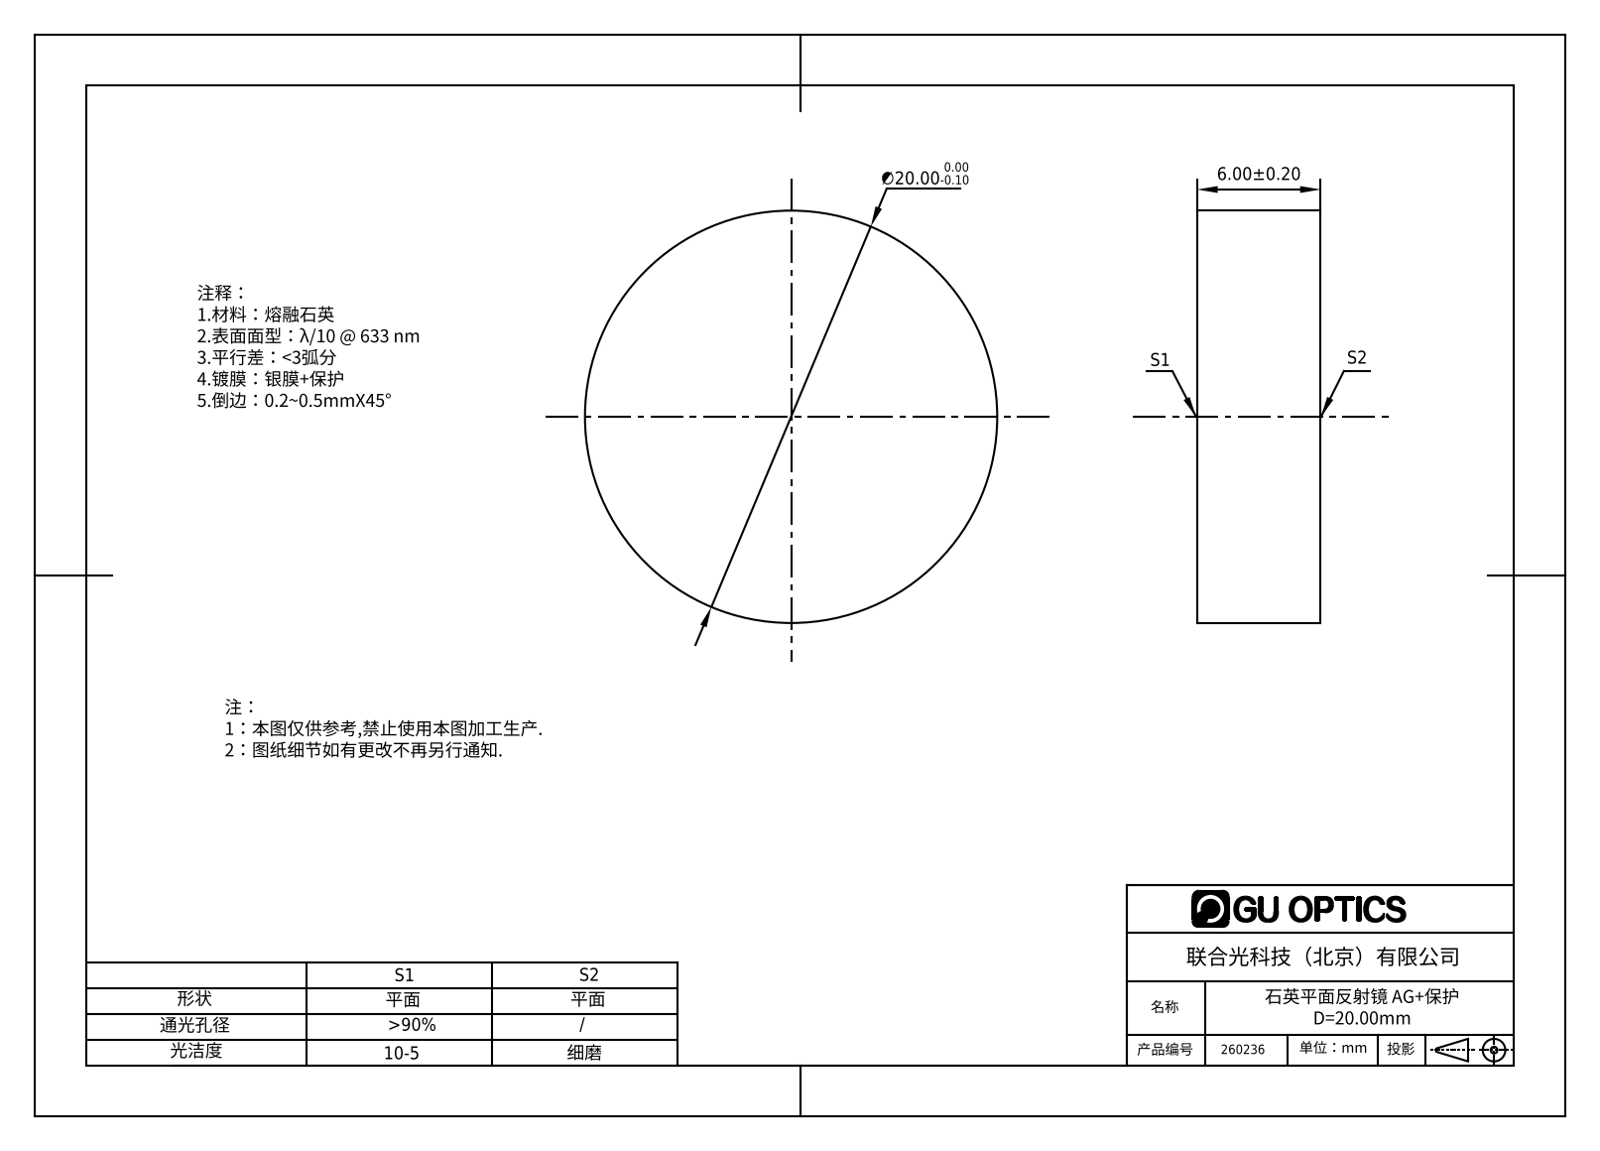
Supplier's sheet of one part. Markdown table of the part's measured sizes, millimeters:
| quantity | value |
| --- | --- |
| part name | 260000 |
| STEP written by | SolidWorks 2016 (AUTOMOTIVE_DESIGN) |
| units | millimeters |
| bodies | 1 solid, 4 faces (2 planar, 2 cylindrical, 0 other) |
| overall size | 20 × 20 × 6 |
| volume | 1 885 mm³ |
| surface area | 1 005 mm² |
| round bosses / shafts (diameter × count) | 20 × 1 |
| main face-to-face distances | 6 |
